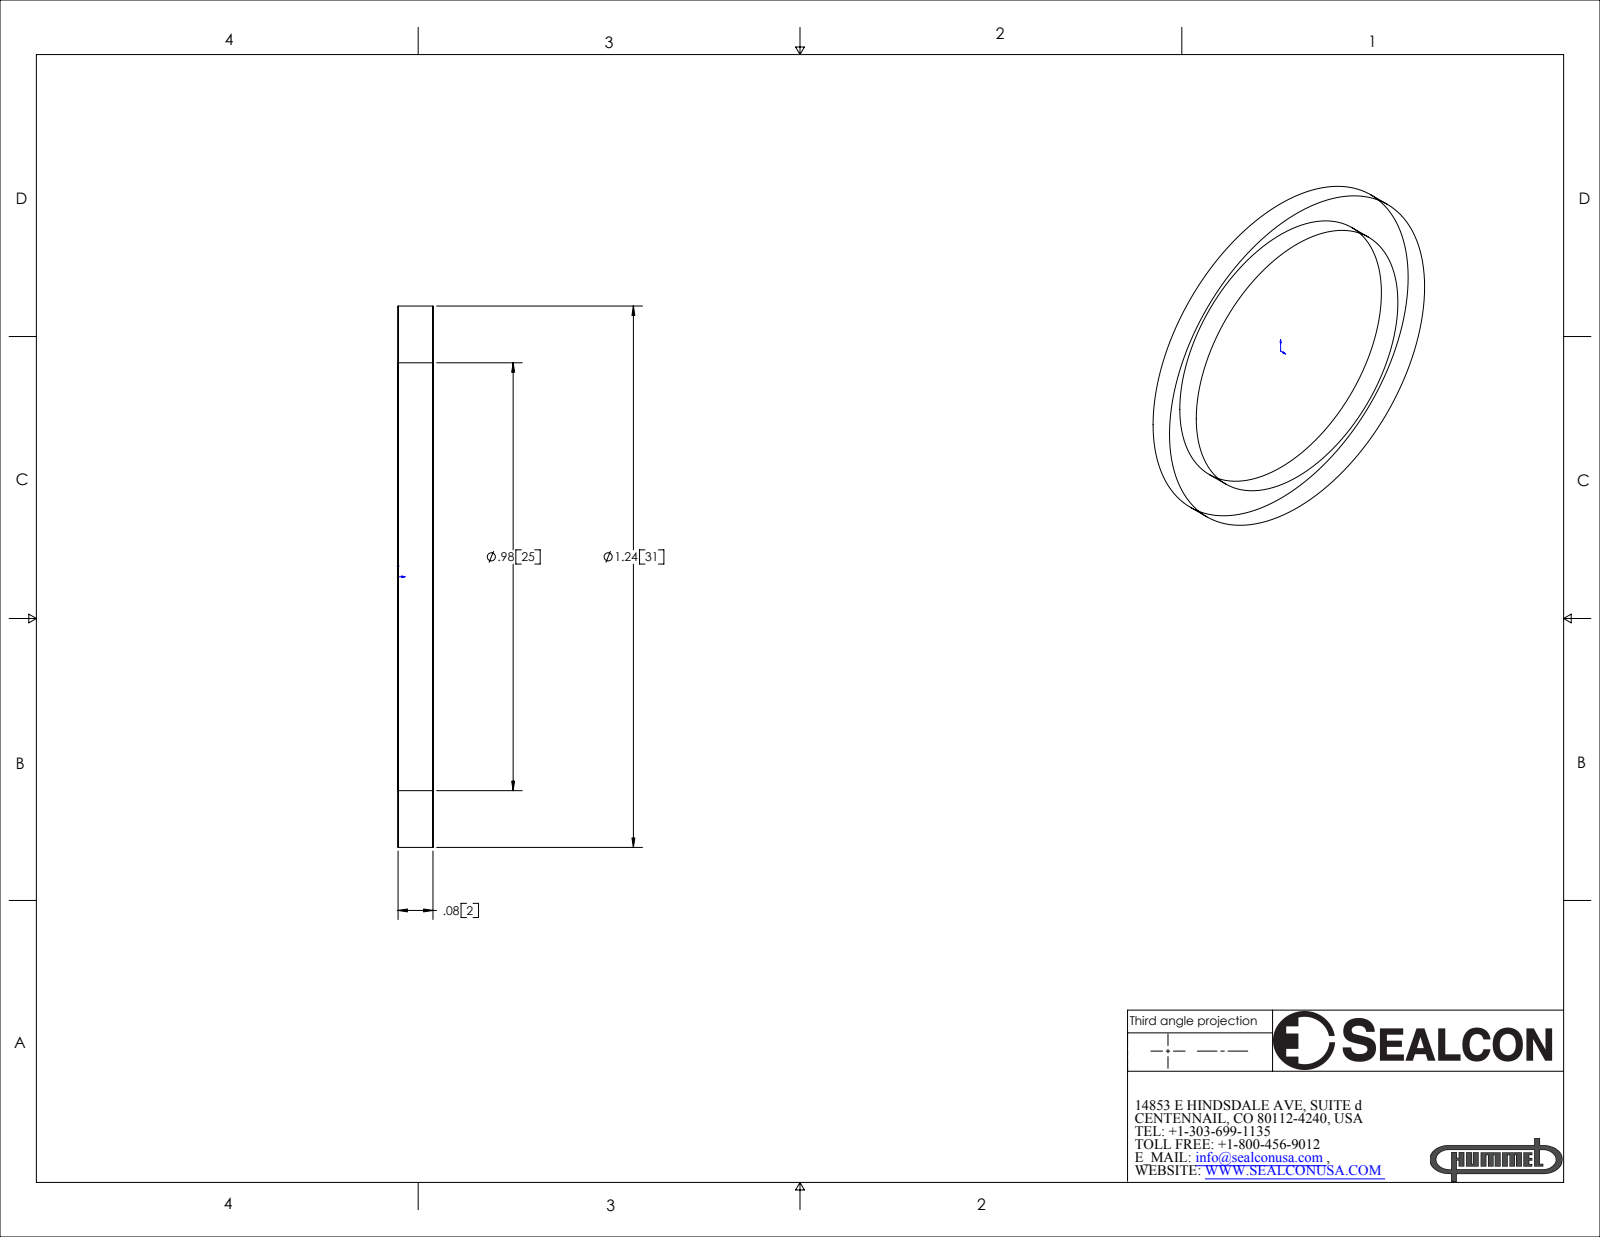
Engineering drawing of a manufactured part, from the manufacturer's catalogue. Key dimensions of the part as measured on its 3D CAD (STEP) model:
Part name (STEP PRODUCT): MS-25-NY
STEP written by: SolidWorks 2007 (CONFIG_CONTROL_DESIGN)
Units: inches
Bodies: 1 solid, 6 faces (2 planar, 4 cylindrical, 0 other)
Overall size (bounding box): 1.24 × 1.24 × 0.08
Volume: 0.036 in³ · Surface area: 1.465 in²
Round holes (diameter × count): ⌀0.98 ×1
Round bosses / shafts (diameter × count): ⌀1.24 ×1
Main face-to-face distances: 0.08
